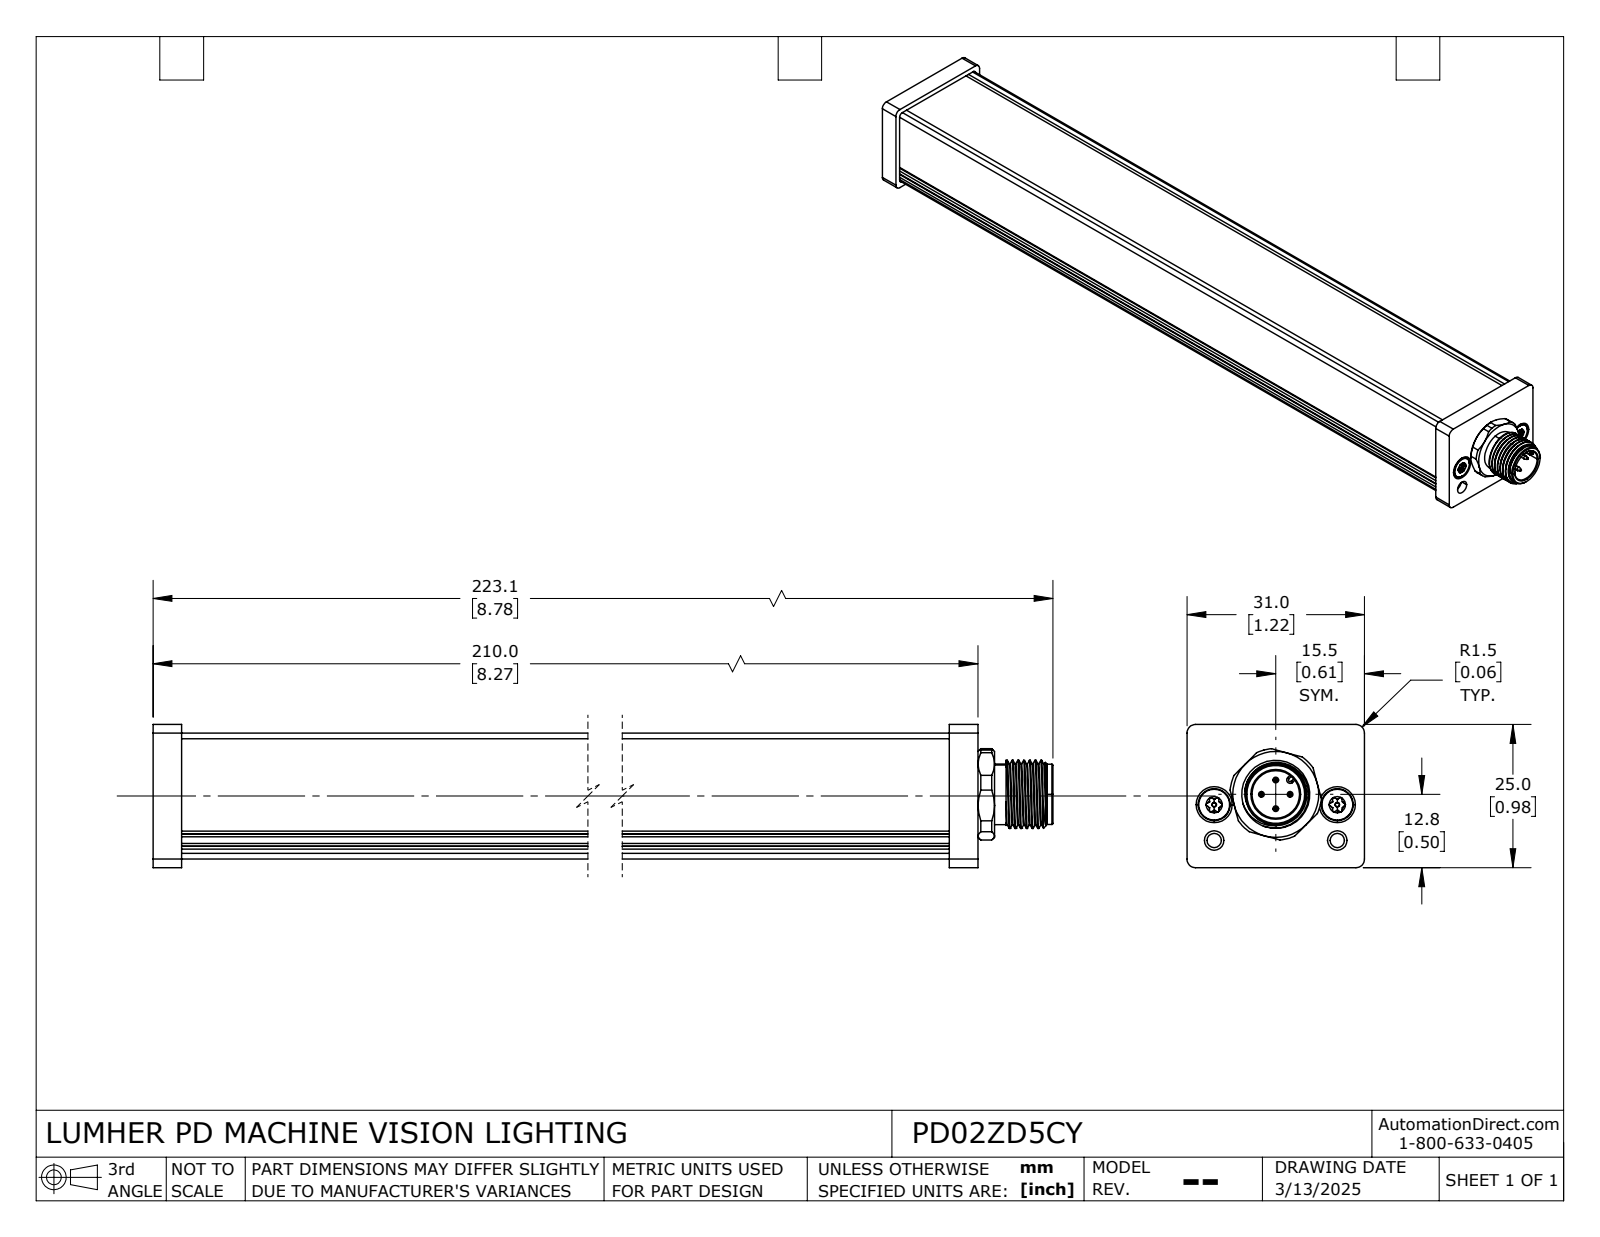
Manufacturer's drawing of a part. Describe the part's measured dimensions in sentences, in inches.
The part is named "PD02__5_Y". Its 3-D file was written by "SolidWorks 2024 (AUTOMOTIVE_DESIGN)". It is 1 solid with 563 faces: 89 planar, 296 cylindrical and 178 other. Overall it measures 8.783 by 1.22 by 0.984 inches. Its volume is 7.63 cubic inches and its surface area 49.73 square inches. Round holes: 4 of diameter 0.057, 4 of diameter 0.134, 2 of diameter 0.098, 1 of diameter 0.327, 1 of diameter 0.37. Round bosses or shafts: 4 of diameter 0.055, 4 of diameter 0.039, 2 of diameter 0.22, 2 of diameter 0.118, 2 of diameter 0.031, 1 of diameter 0.469, 1 of diameter 0.417, 1 of diameter 0.413. Partial cylindrical surfaces (rounded edges, fillets, slot ends): 24 of radius 0.022, 12 of radius 0.01, 8 of radius 0.02, 8 of radius 0.039, 6 of radius 0.118, 4 of radius 0.059, 2 of radius 0.012, 2 of radius 0.04. The main face-to-face distances are 1.102, 0.039, 0.079, 0.059, 0.118, 8.071, 8.189, 8.15, 1.063, 0.098. The hole center spacings are 0.098, 0.139, 0.197, 0.246, 0.332, 0.424, 0.429, 0.454.
